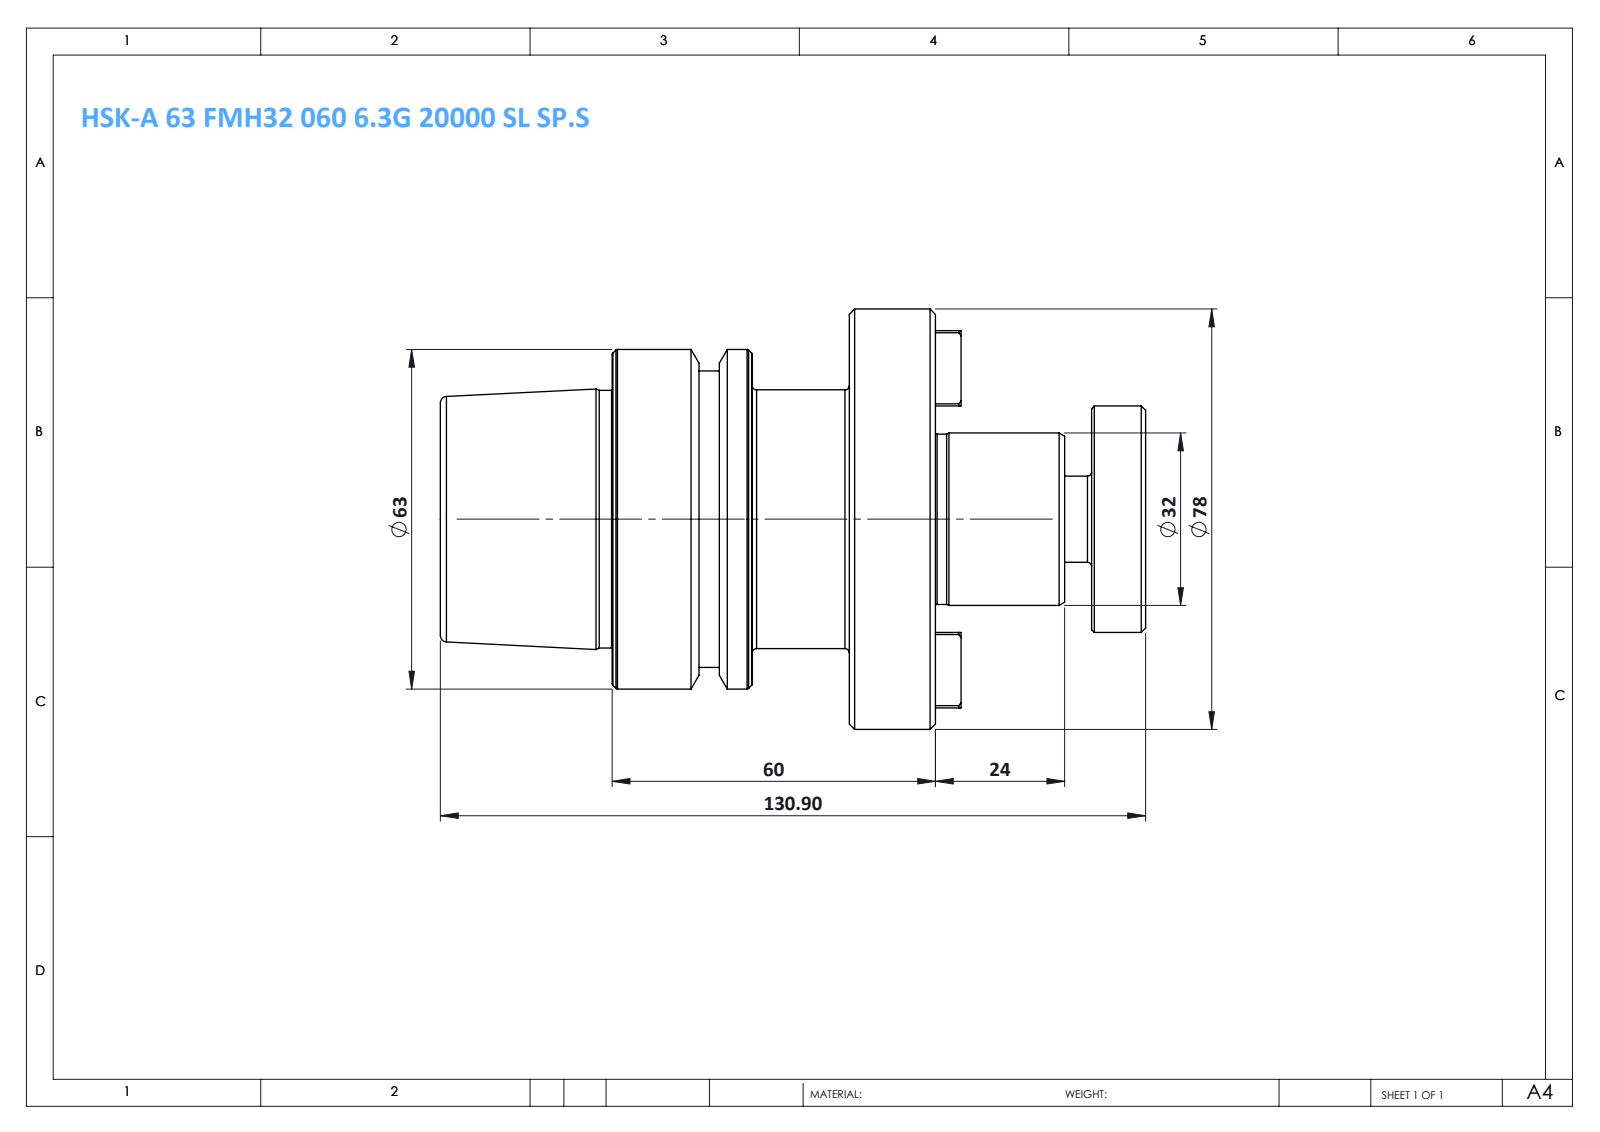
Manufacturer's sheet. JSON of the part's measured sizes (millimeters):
{"part_name": "HSK-A 63 FMH32 060 6.3G 20000 SL SP", "step_written_by": "SolidWorks 2014 (CONFIG_CONTROL_DESIGN)", "units": "millimeters", "bodies": {"solids": 1, "faces": 104, "planar": 36, "cylindrical": 20, "other": 48}, "overall_size": [130.9, 78, 78], "volume_mm3": 277271, "surface_area_mm2": 35558, "round_bosses_or_shafts": [[78, 1], [63, 1], [55, 1], [48, 1], [47.78, 1], [42, 1], [32, 1], [31.6, 1]], "face_to_face_distances": [16, 91.9, 75.9, 39, 55, 130.9, 10, 29, 45, 120.9]}
